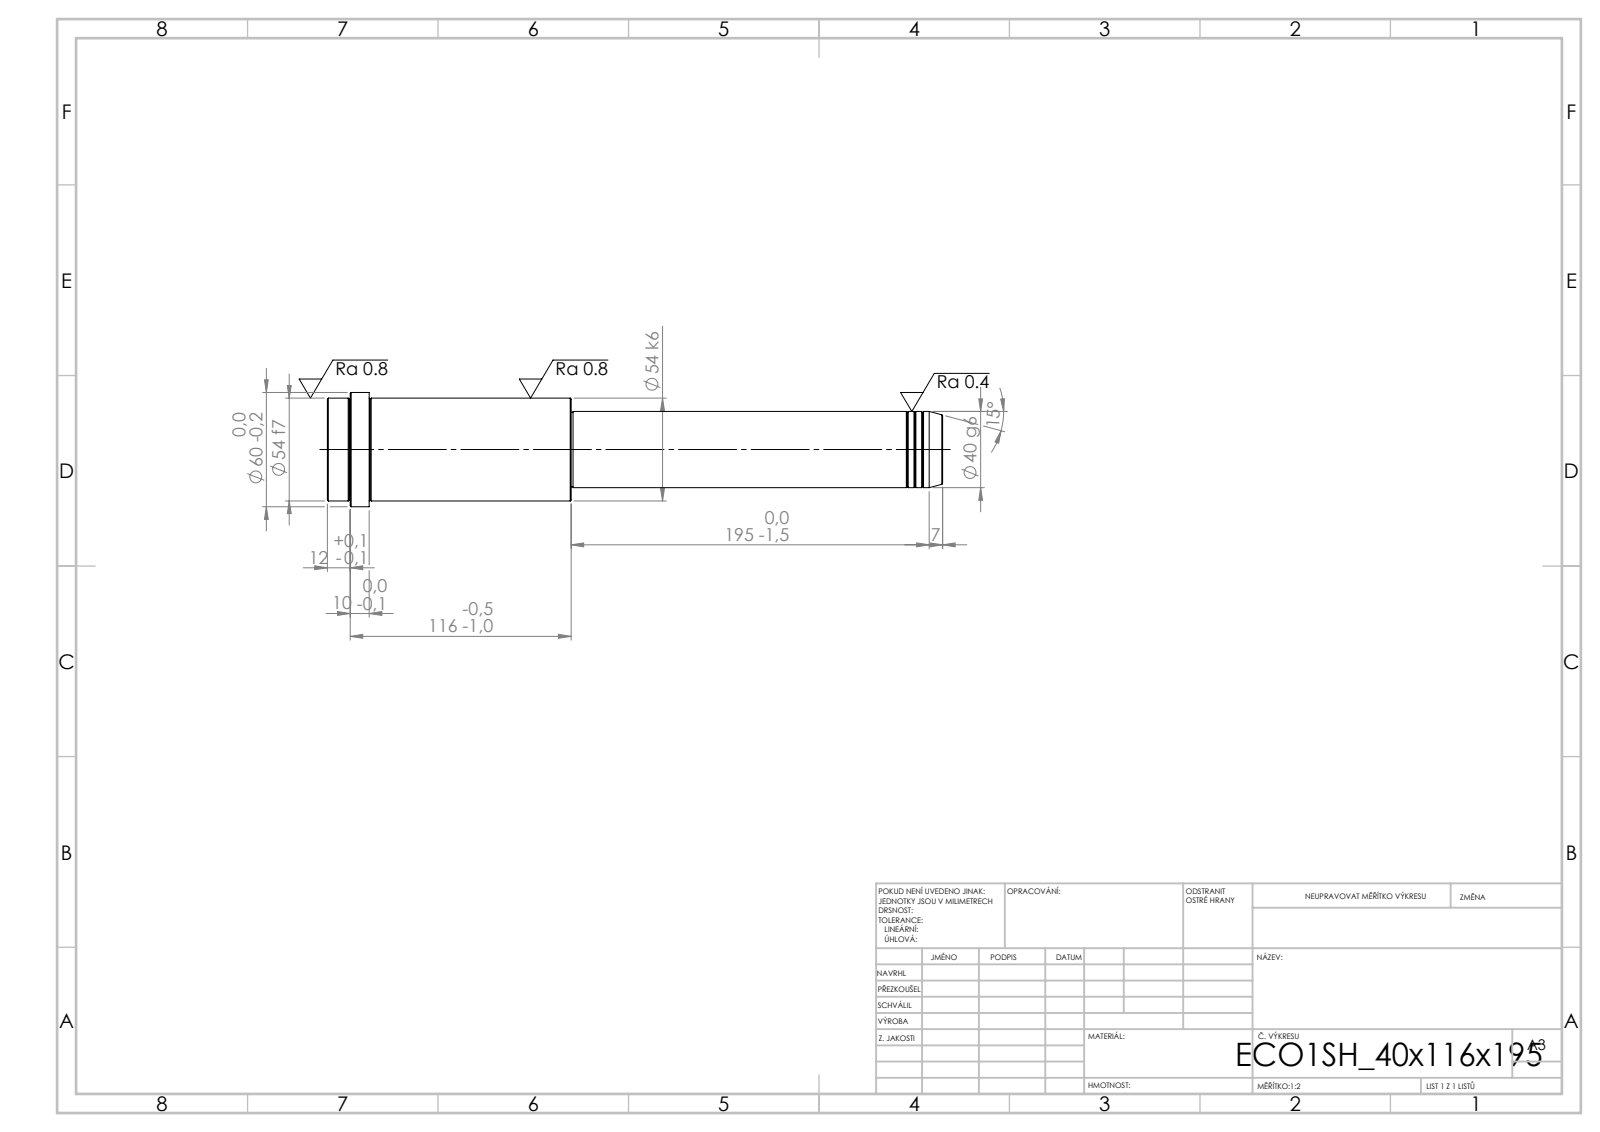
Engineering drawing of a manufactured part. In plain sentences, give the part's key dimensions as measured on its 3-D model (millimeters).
Its 3-D file was written by "SolidWorks 2019 (CONFIG_CONTROL_DESIGN)". It is 1 solid with 52 faces: 6 planar, 16 cylindrical and 30 other. Overall it measures 323 by 60 by 60 millimeters. Its volume is 542 356 cubic millimeters and its surface area 52 172 square millimeters. Round bosses or shafts: 1 of diameter 60, 1 of diameter 54, 1 of diameter 40, 1 of diameter 39. The main face-to-face distances are 128, 195, 323, 301, 106, 22, 311, 116, 10, 12.
